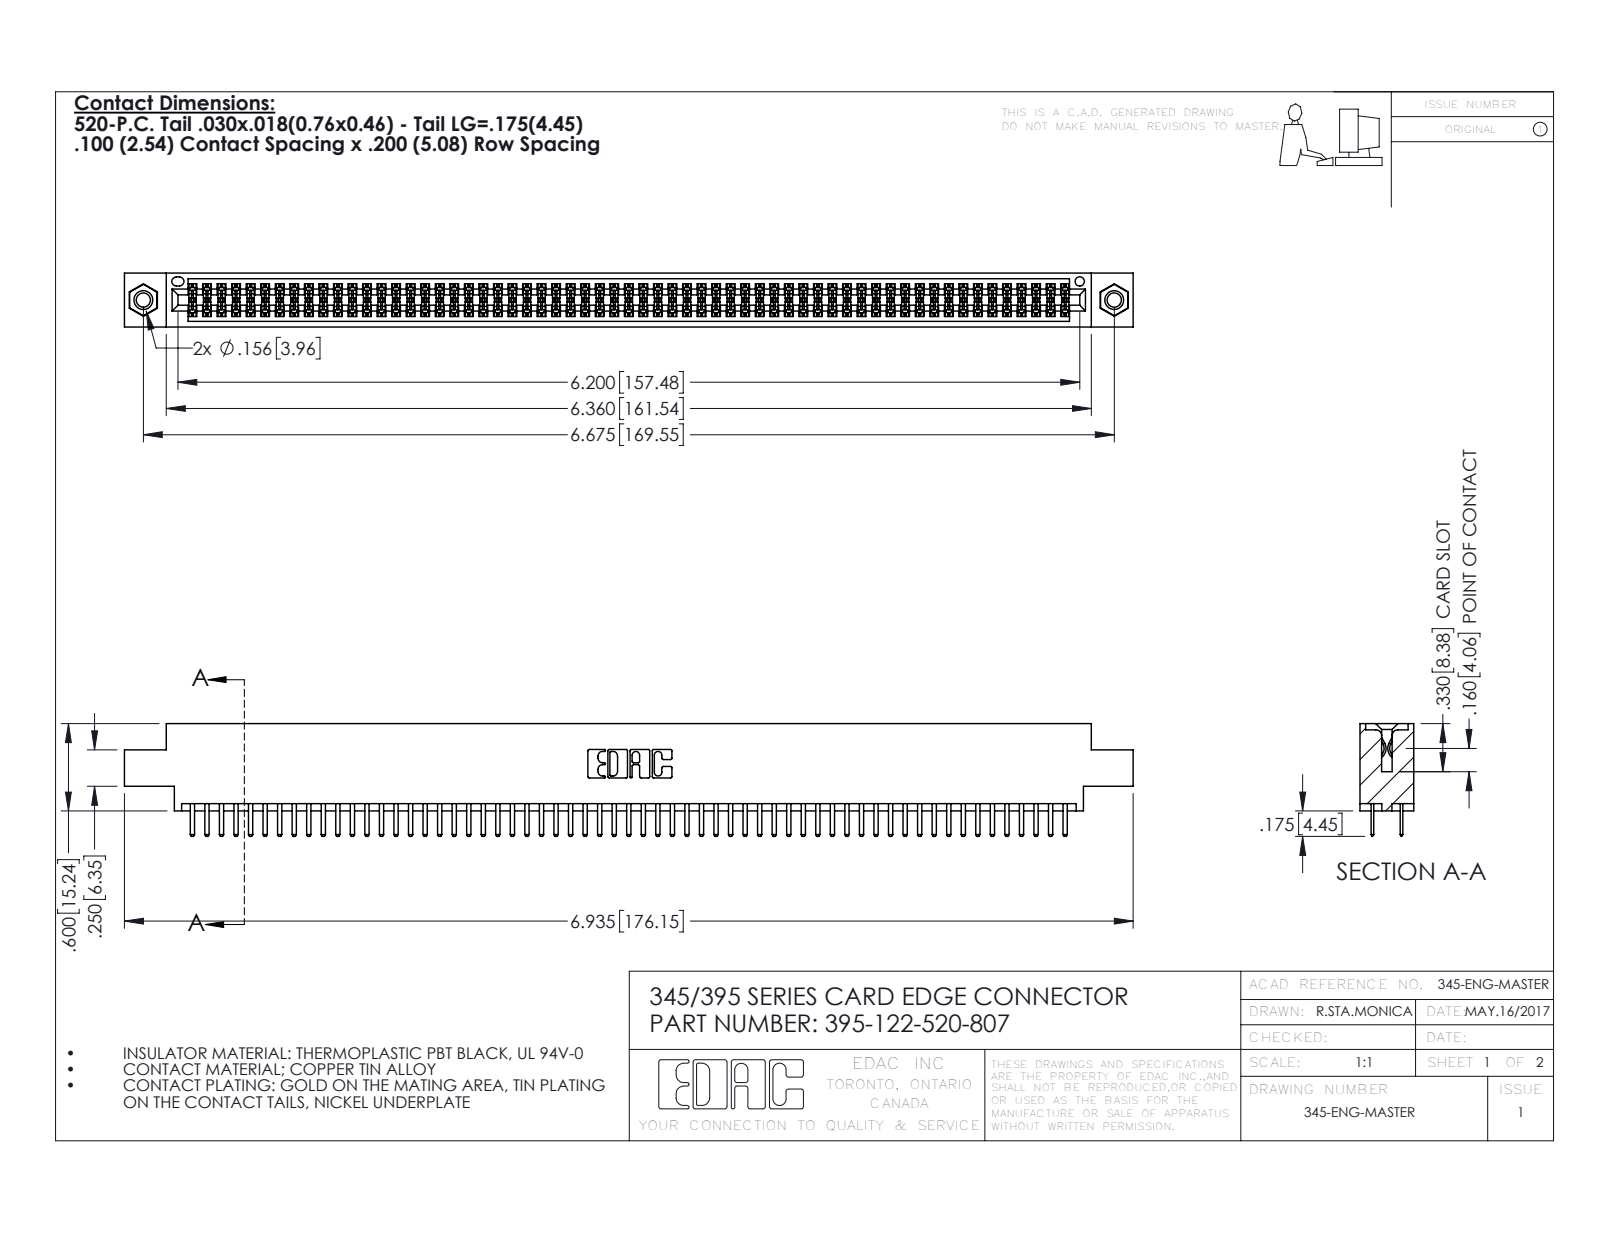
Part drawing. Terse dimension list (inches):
name: 395-122-520-807; 345 Part_0.170 Offset - 0.156 Dia-TI; 345-250-001_345-250-005-103; 345-292-001_345-293-120
written by: SolidWorks 2016 (CONFIG_CONTROL_DESIGN)
unit: in
bodies: 125 solids, 6778 faces (4386 planar, 2376 cylindrical, 16 other)
size: 6.935 × 0.775 × 0.37
volume: 1.044 in³; area: 39.85 in²
holes: 2× ⌀0.098, 2× ⌀0.125, 2× ⌀0.156, 1× ⌀0.064
bosses: 2× ⌀0.155
rounds: 183× R0.006, 126× R0.01, 22× R0.01, 6× R0.007, 6× R0.031, 3× R0.026, 2× R0.014, 2× R0.019
face distances: 0.072, 0.298, 0.2, 0.37, 0.098, 0.272, 0.025, 0.225, 0.022, 0.072
hole spacings: 0.27, 6.439, 6.675
